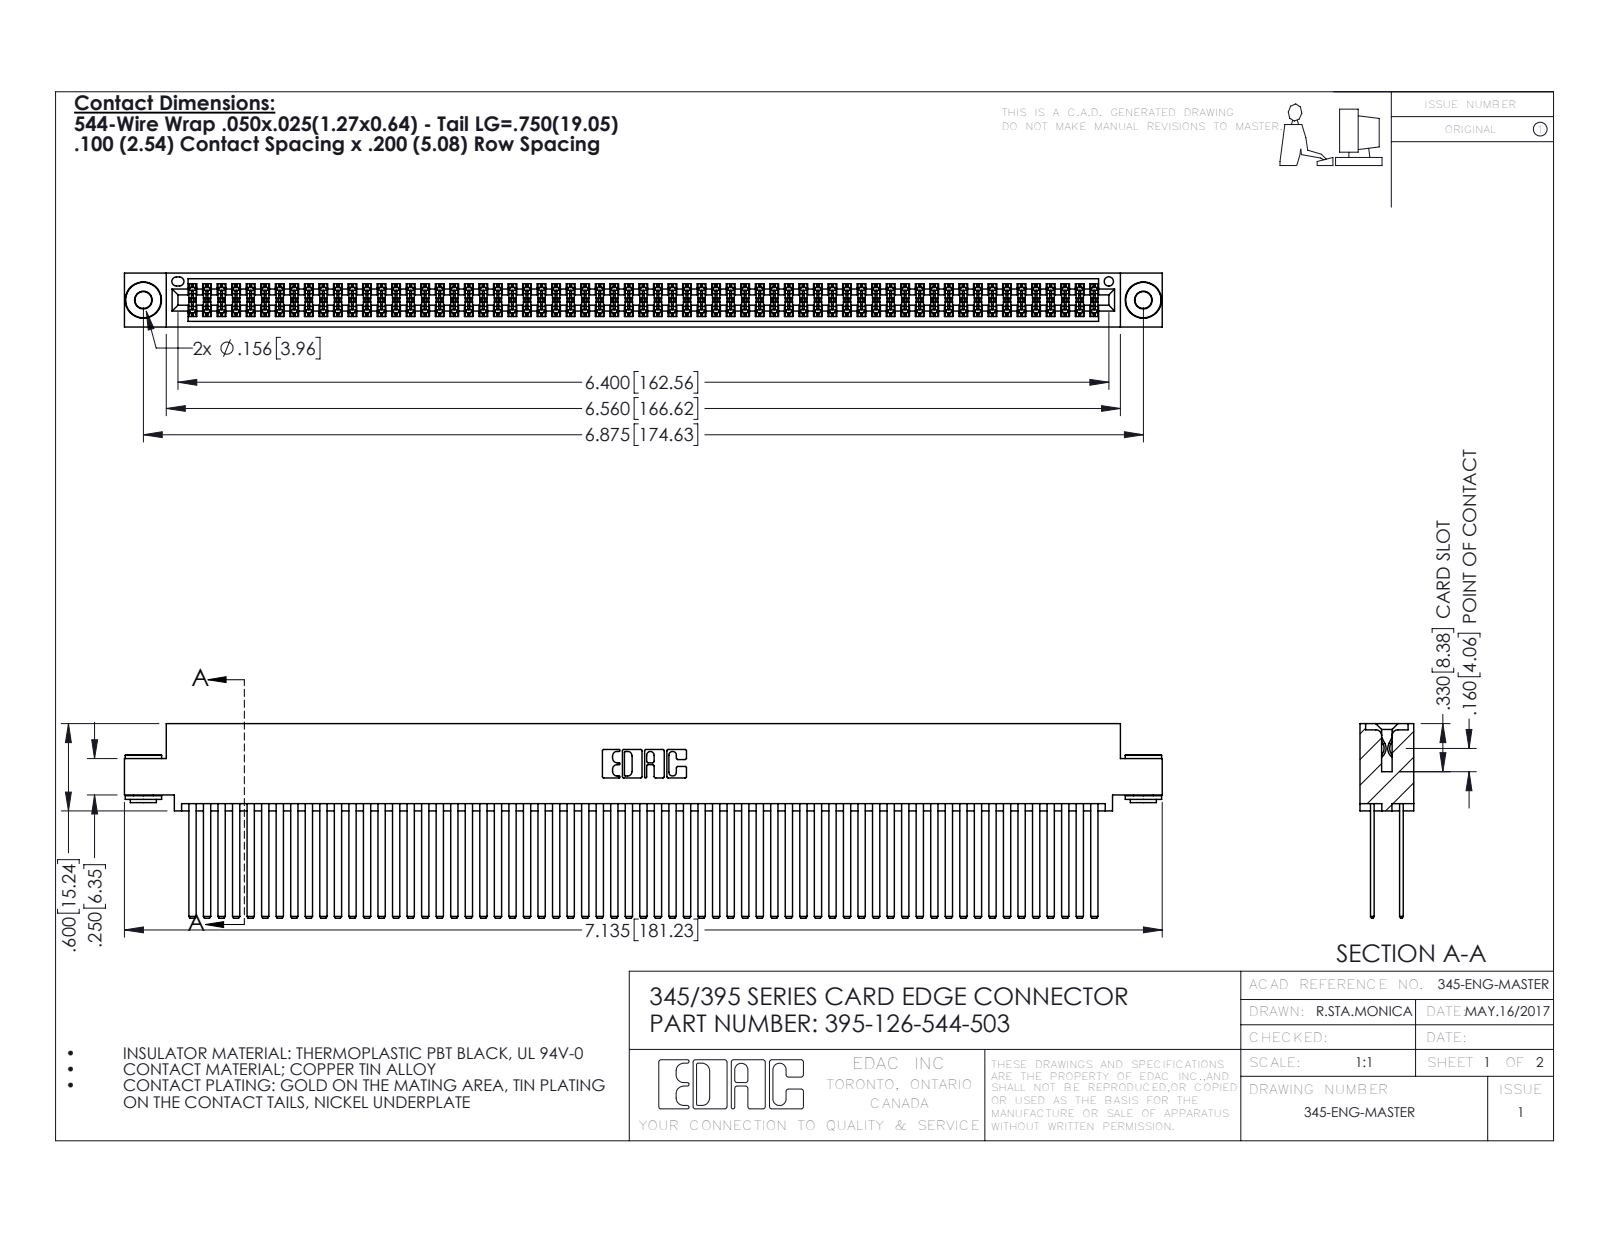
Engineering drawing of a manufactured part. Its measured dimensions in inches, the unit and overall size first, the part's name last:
Units: inches
Overall size (bounding box): 7.135 × 1.337 × 0.37
Round holes (diameter × count): ⌀0.116 ×2, ⌀0.156 ×2, ⌀0.064 ×1
Round bosses / shafts (diameter × count): ⌀0.25 ×2, ⌀0.18 ×2, ⌀0.136 ×2
Partial cylindrical surfaces — rounded edges, fillets, slot ends (radius × count): R0.006 ×189, R0.01 ×22, R0.007 ×6, R0.031 ×6, R0.026 ×3, R0.014 ×2, R0.019 ×2, R0.022 ×2
Main face-to-face distances: 0.2, 0.025, 0.072, 0.098, 0.272, 0.298, 0.225, 0.175, 0.37, 0.149
Hole centre spacings: 0.27, 6.639, 6.875
Volume: 1.191 in³ · Surface area: 53.82 in²
Bodies: 129 solids, 5712 faces (3748 planar, 1956 cylindrical, 8 other)
Part name (STEP PRODUCT): 345 Part_0.110 Offset - 0.156 Dia-TH; 345-292-001_345-293-144; 395-126-544-503; 345-250-002_345-250-002-102
STEP written by: SolidWorks 2016 (CONFIG_CONTROL_DESIGN)
